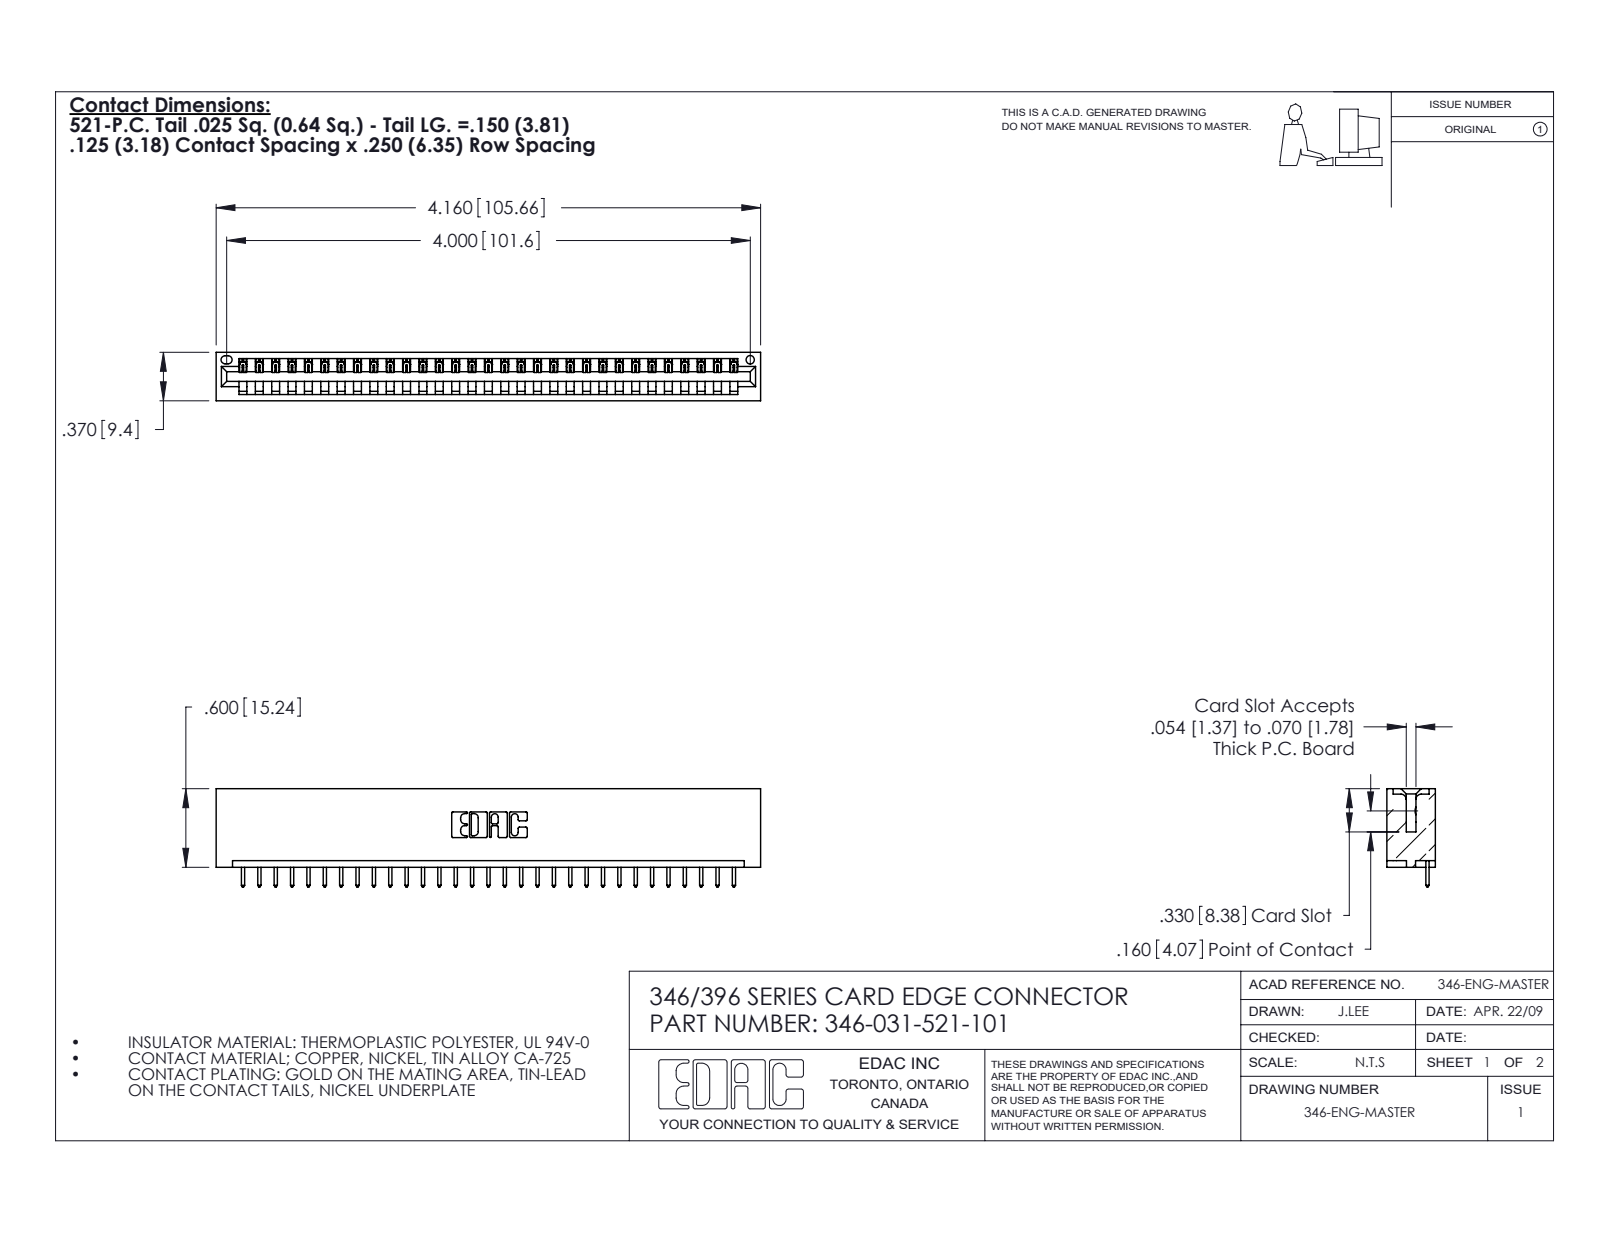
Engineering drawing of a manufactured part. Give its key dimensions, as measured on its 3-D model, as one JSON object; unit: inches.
{"part_name": "346 Part_No Mounting Lugs; 346-031-521-101; 345-292-001_345-293-121", "step_written_by": "SolidWorks 2020 (CONFIG_CONTROL_DESIGN)", "units": "inches", "bodies": {"solids": 32, "faces": 1912, "planar": 1312, "cylindrical": 600, "other": 0}, "overall_size": [4.16, 0.75, 0.37], "volume_in3": 0.641, "surface_area_in2": 19.73, "round_holes": [[0.064, 1]], "partial_cylinders_radius": [[0.006, 62], [0.01, 62], [0.01, 22], [0.007, 6], [0.031, 6], [0.026, 3], [0.031, 2], [0.04, 2]], "face_to_face_distances": [0.048, 0.322, 0.37, 0.25, 0.072, 0.298, 0.025, 0.148, 0.222, 0.1]}
